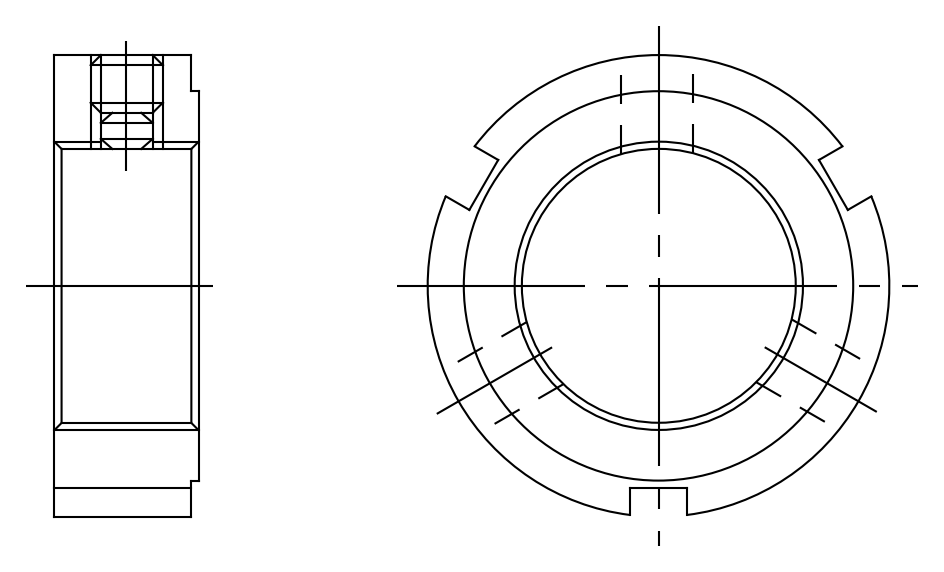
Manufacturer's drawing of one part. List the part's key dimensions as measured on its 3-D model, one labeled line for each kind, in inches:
Part name (STEP PRODUCT): FKD ZMT 20
STEP written by: Autodesk Inventor 2011 (AUTOMOTIVE_DESIGN)
Units: inches
Bodies: 1 solid, 20 faces (12 planar, 8 cylindrical, 0 other)
Overall size (bounding box): 1.26 × 1.255 × 0.394
Volume: 0.264 in³ · Surface area: 4.371 in²
Round holes (diameter × count): ⌀0.163 ×3, ⌀0.787 ×1
Round bosses / shafts (diameter × count): ⌀1.26 ×1, ⌀1.063 ×1
Main face-to-face distances: 0.394, 0.02, 0.374, 0.157
